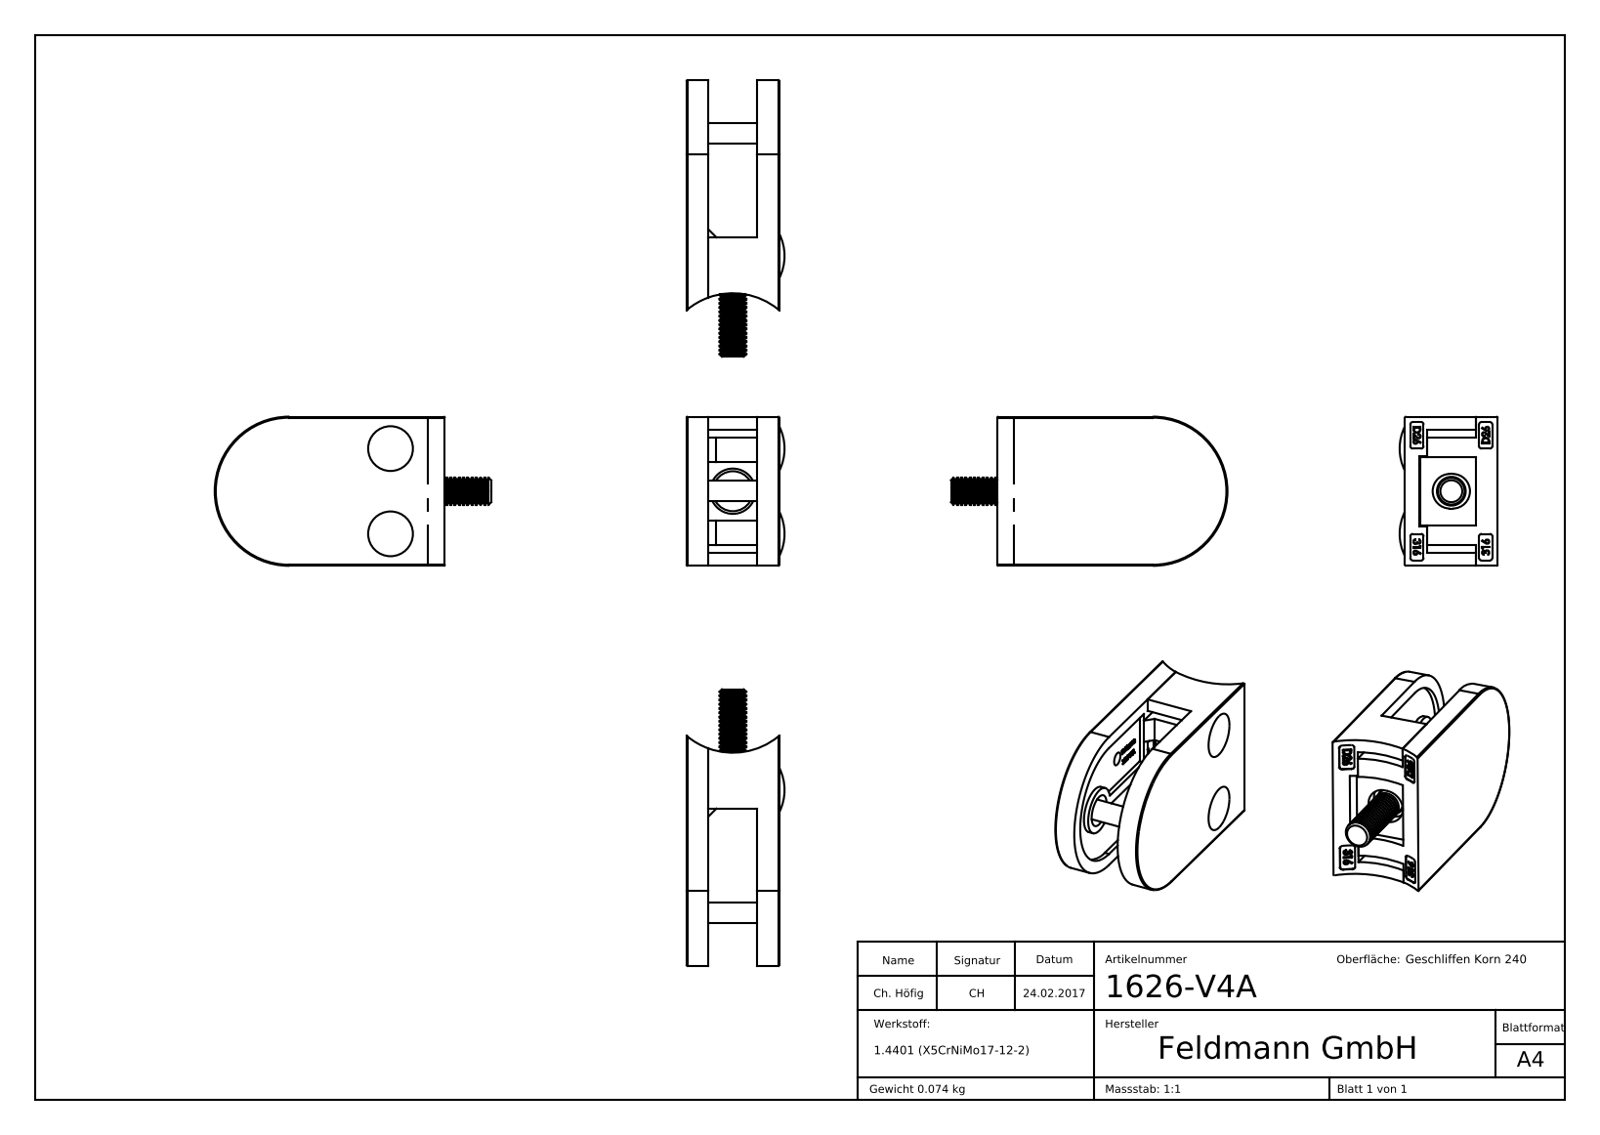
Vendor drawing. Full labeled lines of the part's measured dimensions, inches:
Part name (STEP PRODUCT): 16-Stift_16-Stift; socket head thin cap screw_din_DIN 7984 - M5 x 16 --- 16S; 16-Kappe_16-Kappe; 16xx-XXX Teil2_1626-V4A (+3 more)
STEP written by: SolidWorks 2015 (CONFIG_CONTROL_DESIGN)
Units: inches
Bodies: 8 solids, 1387 faces (638 planar, 204 cylindrical, 545 other)
Overall size (bounding box): 2.043 × 1.102 × 0.724
Volume: 0.607 in³ · Surface area: 14.19 in²
Round holes (diameter × count): ⌀0.039 ×2, ⌀0.098 ×2, ⌀0.13 ×2, ⌀0.163 ×2, ⌀0.323 ×2, ⌀0.154 ×1, ⌀0.236 ×1
Round bosses / shafts (diameter × count): ⌀0.301 ×2, ⌀0.157 ×2, ⌀0.098 ×2, ⌀0.346 ×1, ⌀0.335 ×1, ⌀0.197 ×1, ⌀0.152 ×1
Partial cylindrical surfaces — rounded edges, fillets, slot ends (radius × count): R0.02 ×20, R0.008 ×4, R0.128 ×2, R0.457 ×1, R0.53 ×1, R0.533 ×1, R0.551 ×1
Main face-to-face distances: 0.685, 0.161, 0.524, 0.126, 0.559, 0.035, 0.398, 0.433, 0.362, 0.098
Hole centre spacings: 0.433, 0.555, 0.788, 0.959, 0.496, 0.63
